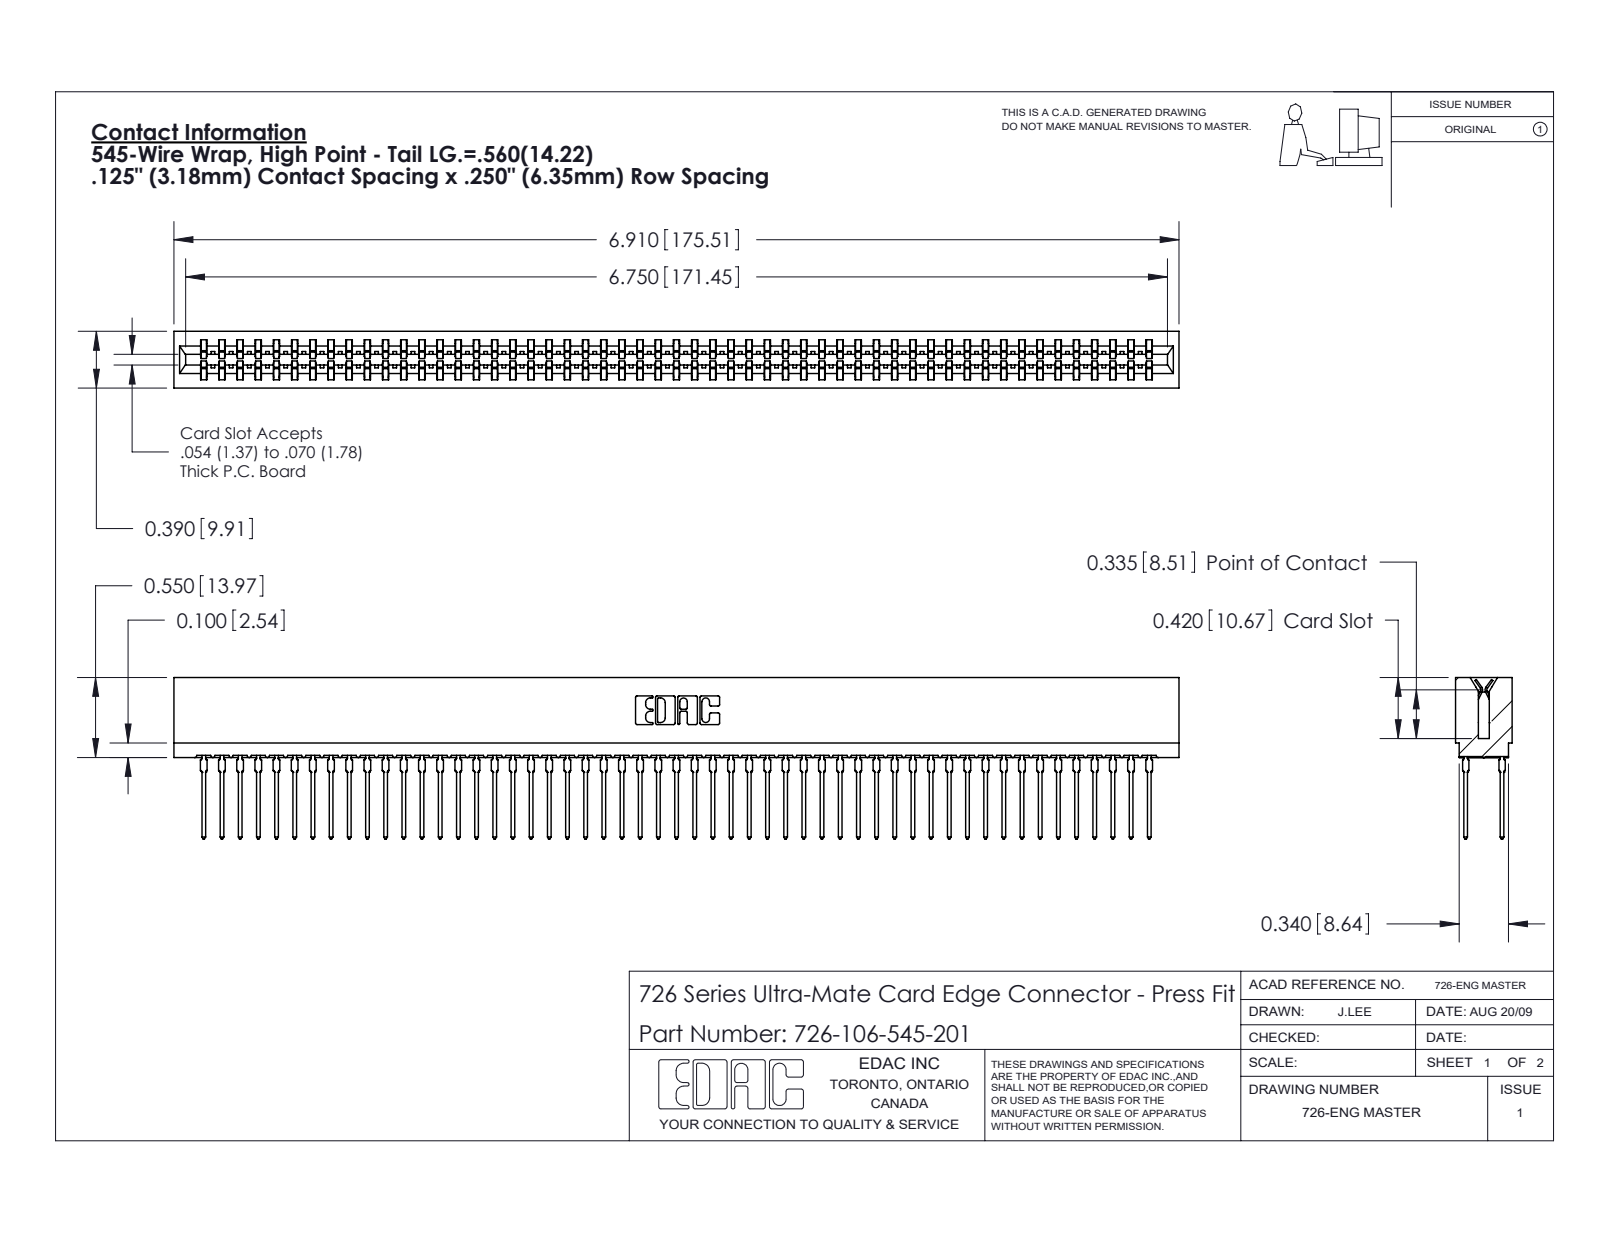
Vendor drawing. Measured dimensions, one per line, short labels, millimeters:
name: 726 Part_.515 Slot Depth - 01; 746-292-001_545; 726-106-545-201
written by: SolidWorks 2020 (CONFIG_CONTROL_DESIGN)
unit: mm
bodies: 107 solids, 9584 faces (4931 planar, 1897 cylindrical, 2756 other)
size: 175.5 × 28.2 × 9.9
volume: 16 450 mm³; area: 29 320 mm²
rounds: 212× R0.5, 54× R0.4, 22× R0.3, 8× R0.1, 8× R0.3, 6× R0.2, 6× R0.8, 3× R0.7
face distances: 1.4, 8.5, 0.6, 7.8, 6.4, 9.9, 2.1, 7, 9.3, 0.8
